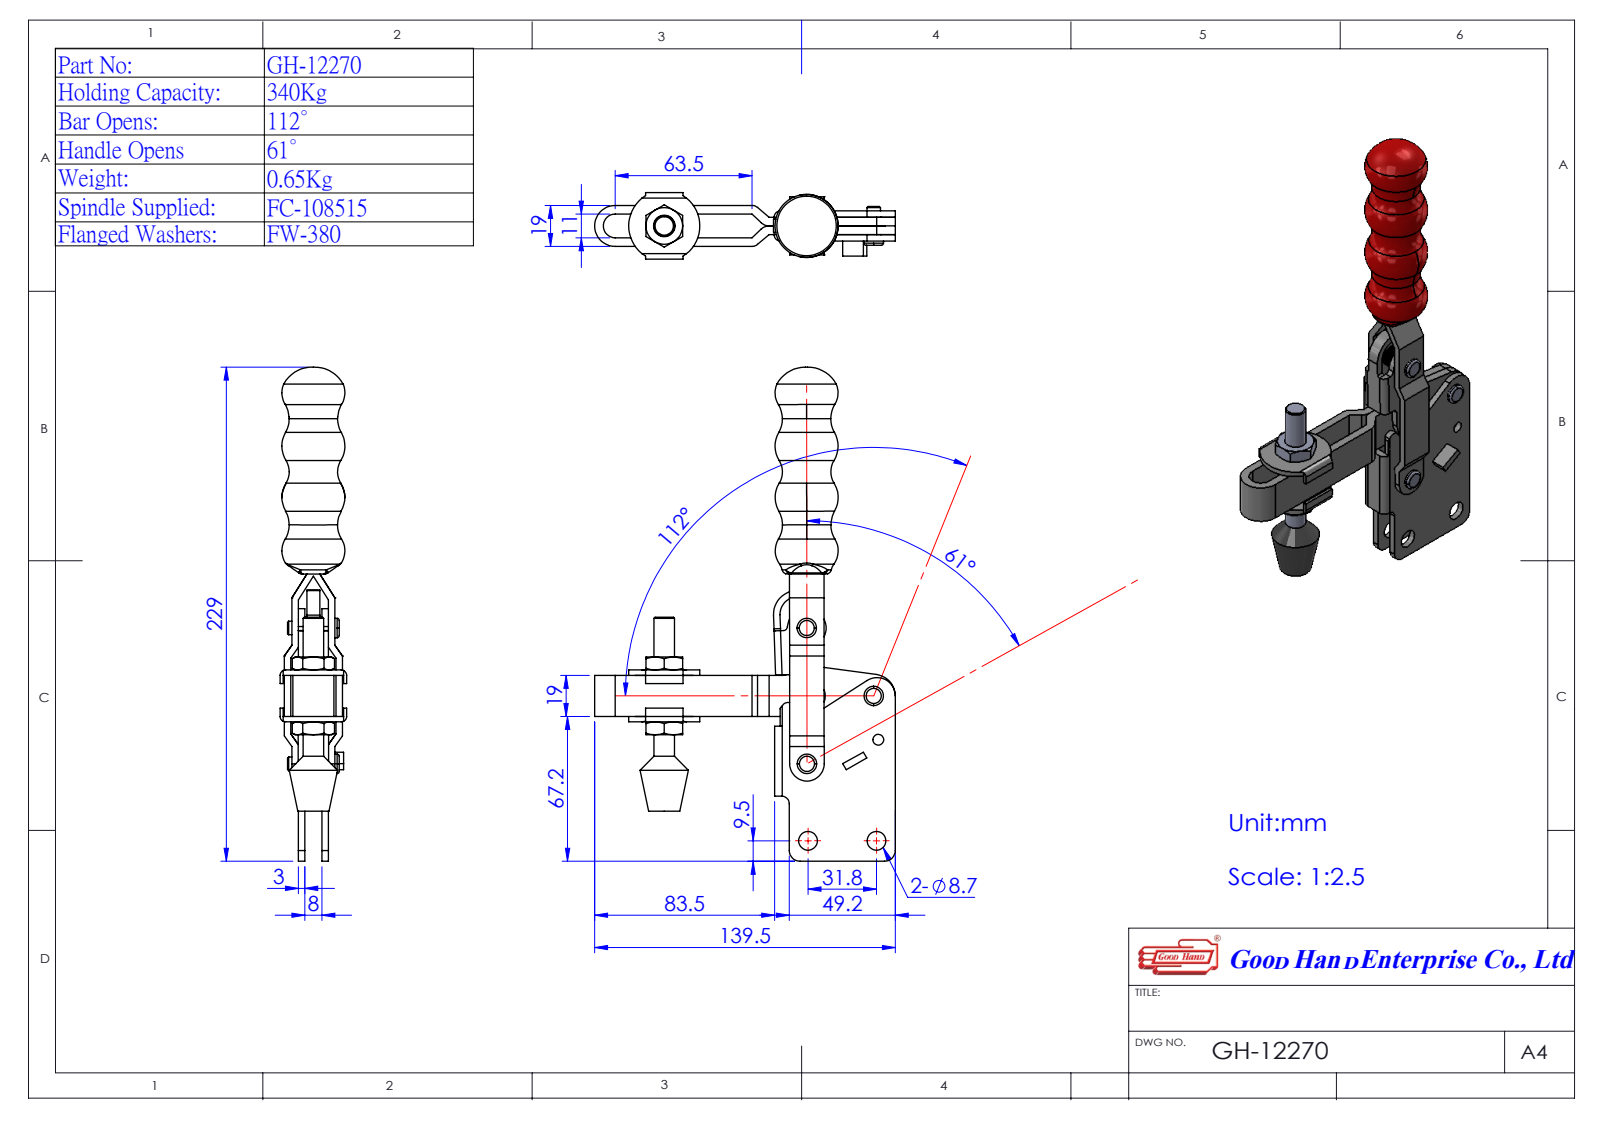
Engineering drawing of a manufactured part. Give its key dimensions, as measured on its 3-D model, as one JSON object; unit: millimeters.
{"part_name": "Group2^GH-12270(簡化)-1; Group1^GH-12270(簡化)-1; GH-12270(簡化)-1; Group4^GH-12270(簡化)-1 (+2 more)", "step_written_by": "SolidWorks 2016 (AUTOMOTIVE_DESIGN)", "units": "millimeters", "bodies": {"solids": 6, "faces": 357, "planar": 148, "cylindrical": 125, "other": 84}, "overall_size": [229.16, 139.5, 30.86], "volume_mm3": 131284, "surface_area_mm2": 62371, "round_holes": [[6, 4], [8.7, 2], [5, 1]], "round_bosses_or_shafts": [[9.01, 4], [6.28, 4], [9.5, 2], [9.53, 1]], "partial_cylinders_radius": [[2, 3], [5.5, 3], [1, 2], [3, 2], [4, 2], [5, 2], [5, 2], [8, 2]], "face_to_face_distances": [3, 11, 4, 8, 14, 9.5, 1.5, 5.5, 7, 19], "hole_center_spacings": [31.52, 20.43, 30, 31.8, 34.96, 35.65, 38.01, 44.2]}
